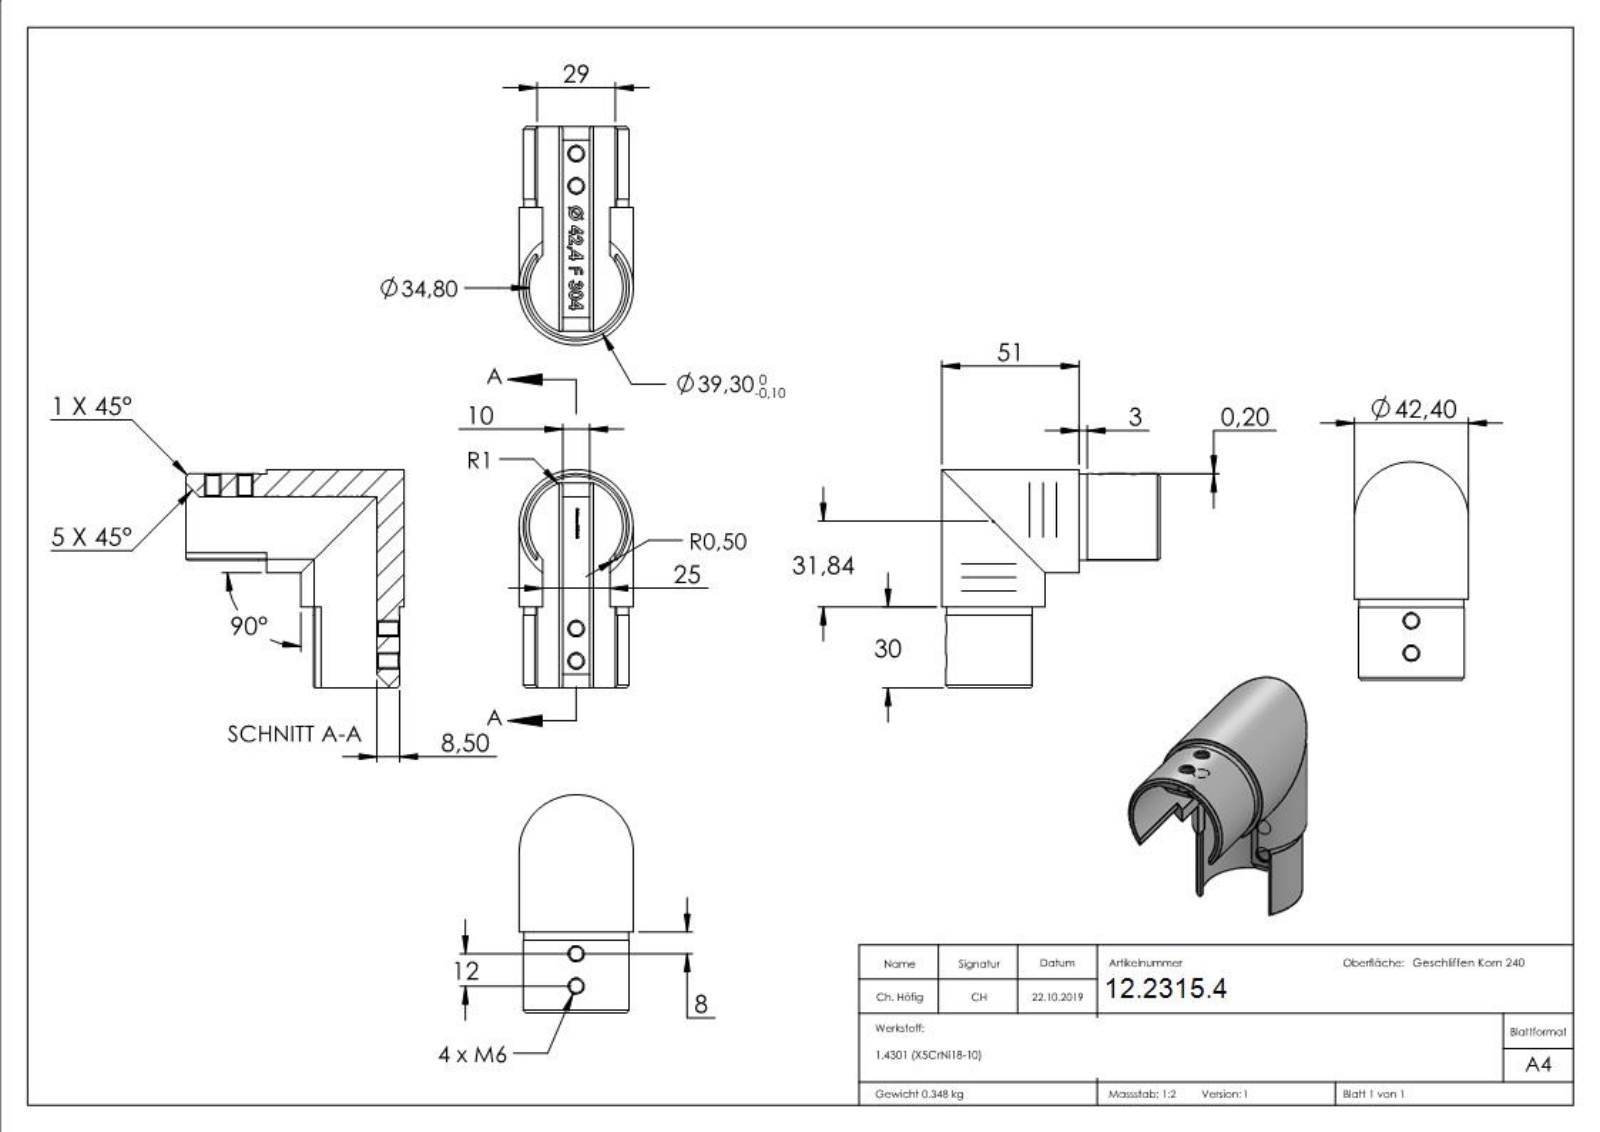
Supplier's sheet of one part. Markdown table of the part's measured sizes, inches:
| quantity | value |
| --- | --- |
| part name | 60320-240 |
| STEP written by | SolidWorks 2015 (CONFIG_CONTROL_DESIGN) |
| units | inches |
| bodies | 1 solid, 408 faces (223 planar, 22 cylindrical, 163 other) |
| overall size | 3.189 × 3.189 × 1.669 |
| volume | 2.681 in³ |
| surface area | 40.12 in² |
| round holes (diameter × count) | 0.197 × 4 |
| round bosses / shafts (diameter × count) | 1.669 × 2 |
| partial cylindrical surfaces (radius × count) | 0.02 × 4, 0.039 × 4, 0.685 × 2, 0.766 × 2, 0.774 × 2 |
| main face-to-face distances | 0.394, 1.612, 1.063, 0.295, 0.689, 0.079, 0.374, 0.768, 2.793, 1.181 |
| hole center spacings | 0.472 |
